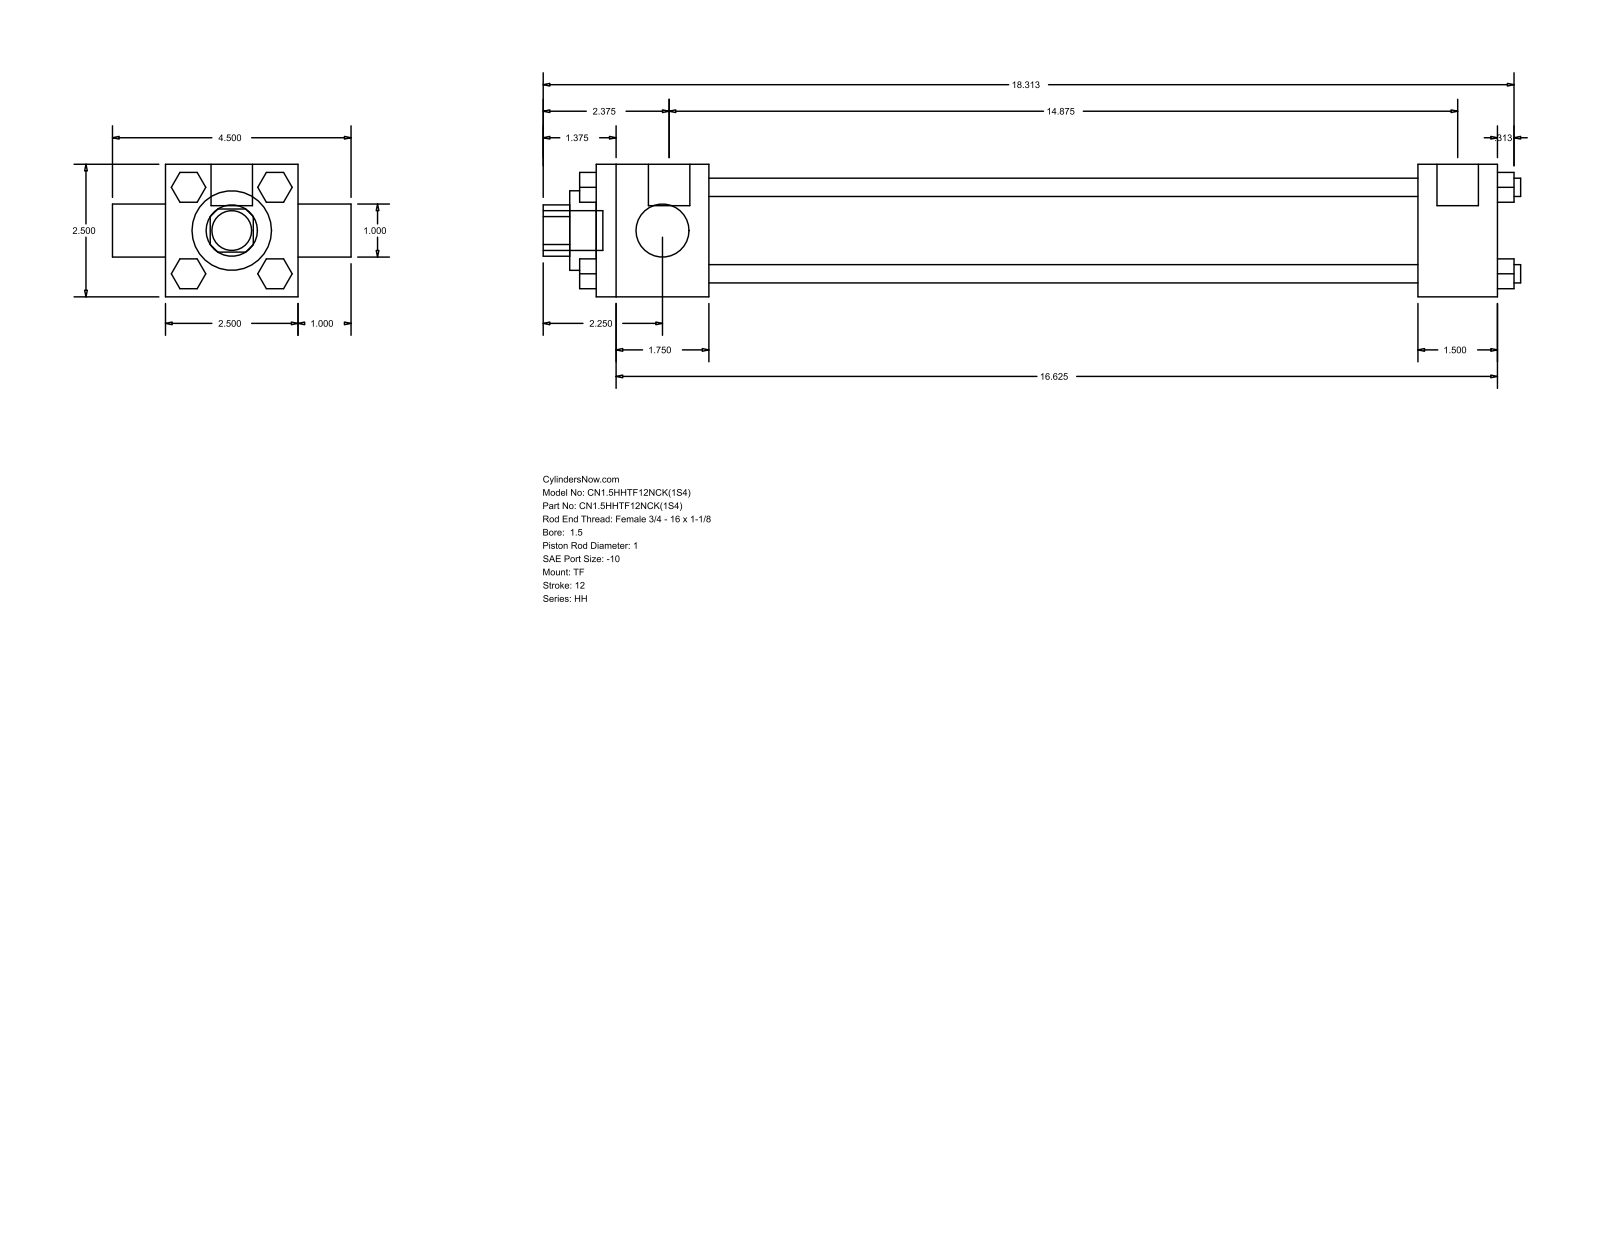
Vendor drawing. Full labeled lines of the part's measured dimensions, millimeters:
Part name (STEP PRODUCT): HH_TF__0150_1
STEP written by: GSSL Pune (CONFIG_CONTROL_DESIGN)
Units: millimetres
Bodies: 0 solids, 120 faces (92 planar, 28 cylindrical, 0 other)
Overall size (bounding box): 468.31 × 114.3 × 63.5
Round holes (diameter × count): ⌀25.4 ×2, ⌀38.1 ×1, ⌀44.45 ×1
Round bosses / shafts (diameter × count): ⌀8.76 ×4, ⌀5.56 ×3, ⌀19.84 ×2, ⌀19.05 ×1
Partial cylindrical surfaces — rounded edges, fillets, slot ends (radius × count): R12.29 ×1
Main face-to-face distances: 63.5, 377.82, 339.72, 38.1, 53.98, 393.7, 431.8, 439.74, 25.4, 20.7
